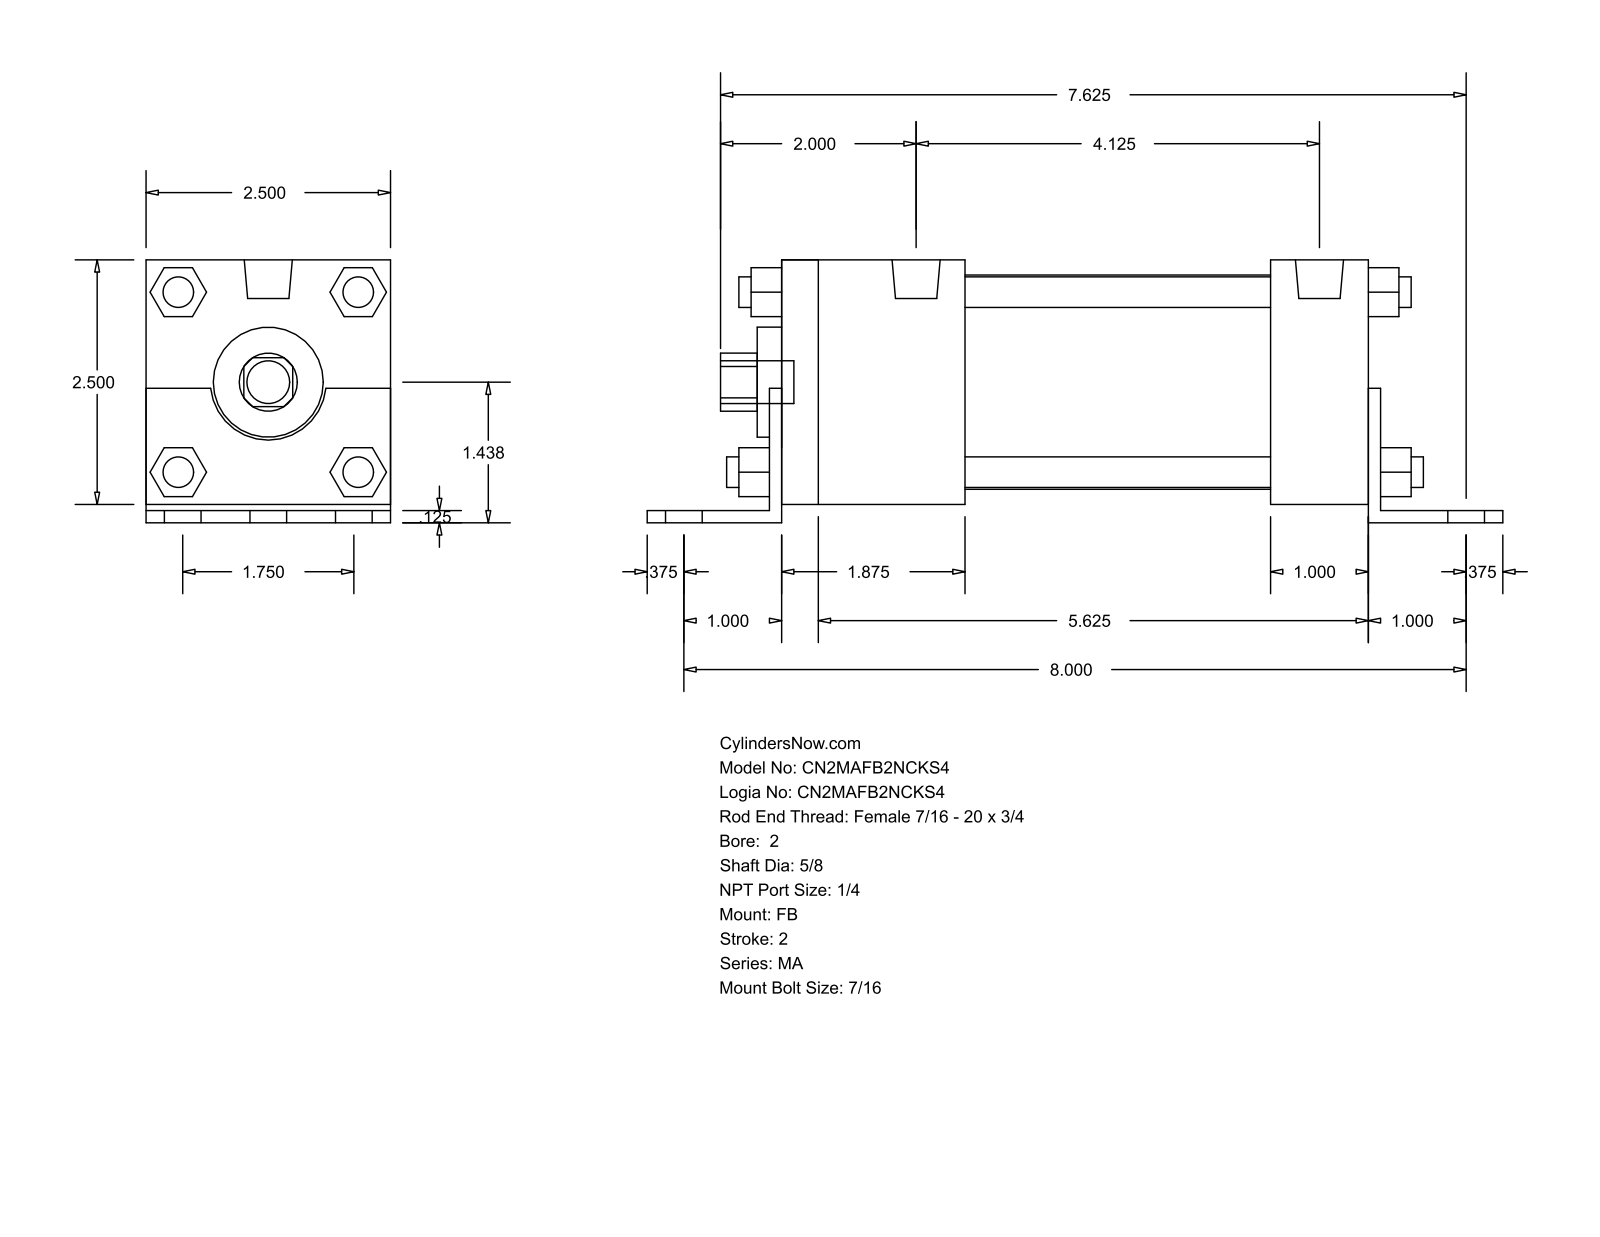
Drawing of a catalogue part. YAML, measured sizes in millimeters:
part_name: "MA_FB__0200_0.625"
step_written_by: "GSSL Pune (CONFIG_CONTROL_DESIGN)"
units: millimeters
bodies: {solids: 0, faces: 140, planar: 105, cylindrical: 35, other: 0}
overall_size: [222.25, 68.26, 63.5]
round_holes:
  - {diameter: 15.88, count: 1}
  - {diameter: 28.57, count: 1}
  - {diameter: 55.63, count: 1}
round_bosses_or_shafts:
  - {diameter: 7.94, count: 8}
  - {diameter: 11.11, count: 7}
  - {diameter: 12.49, count: 2}
partial_cylinders:
  - {radius: 7.54, count: 1}
  - {radius: 15.05, count: 1}
face_to_face_distances: [63.5, 3.17, 4.76, 68.26, 1.59, 65.09, 152.4, 158.75, 3.18, 155.57]
